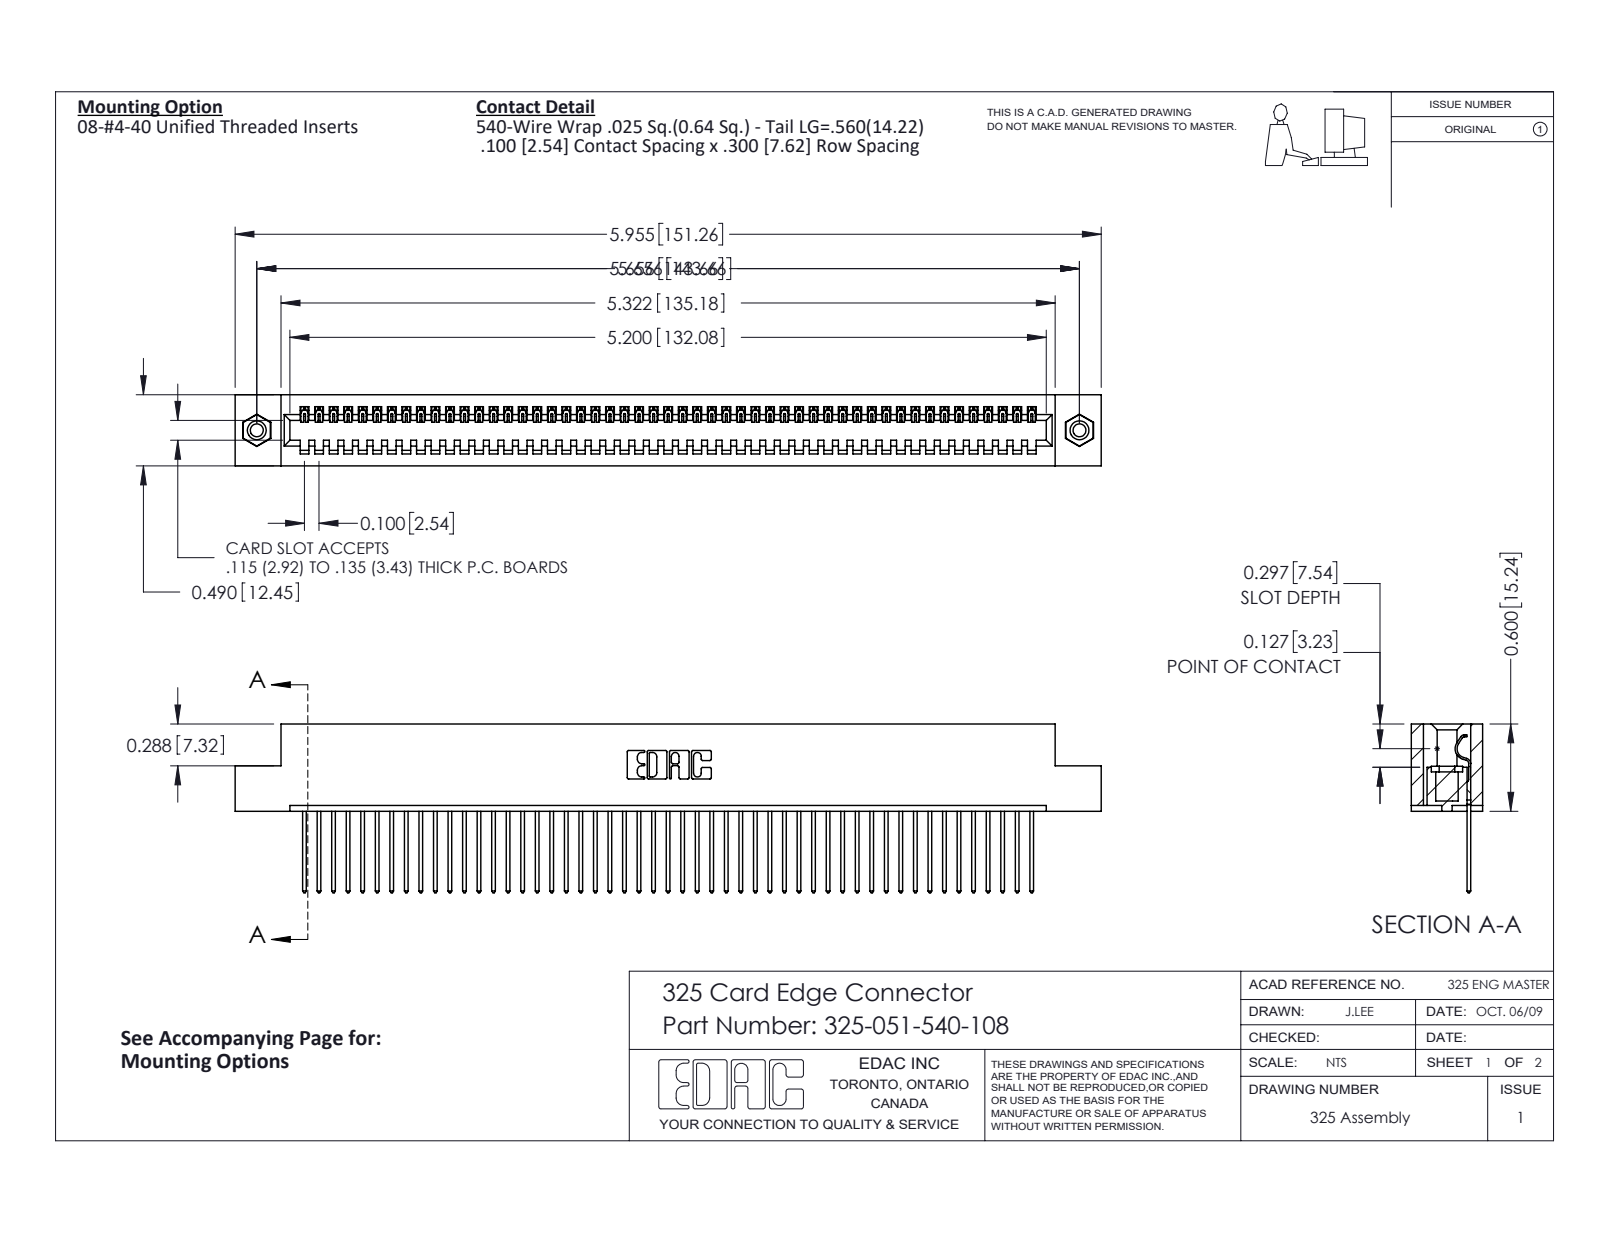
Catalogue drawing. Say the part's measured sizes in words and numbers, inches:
The part is named "325-292-001_325-293-140; 325 Part_TI; 325-051-540-108; 345-250-001_345-250-003-102". Its 3-D file was written by "SolidWorks 2016 (CONFIG_CONTROL_DESIGN)". It is 54 solids with 3132 faces: 2244 planar, 872 cylindrical and 16 other. Overall it measures 5.955 by 1.16 by 0.49 inches. Its volume is 1.18 cubic inches and its surface area 33.79 square inches. Round holes: 2 of diameter 0.089, 2 of diameter 0.125, 2 of diameter 0.16. Round bosses or shafts: 2 of diameter 0.155. Partial cylindrical surfaces (rounded edges, fillets, slot ends): 102 of radius 0.006, 102 of radius 0.01, 22 of radius 0.01, 6 of radius 0.007, 6 of radius 0.031, 3 of radius 0.026, 1 of radius 0.014, 1 of radius 0.022. The main face-to-face distances are 0.083, 0.407, 0.49, 0.3, 0.107, 0.383, 0.025, 0.325, 0.56, 0.263. The hole center spacings are 5.656.
